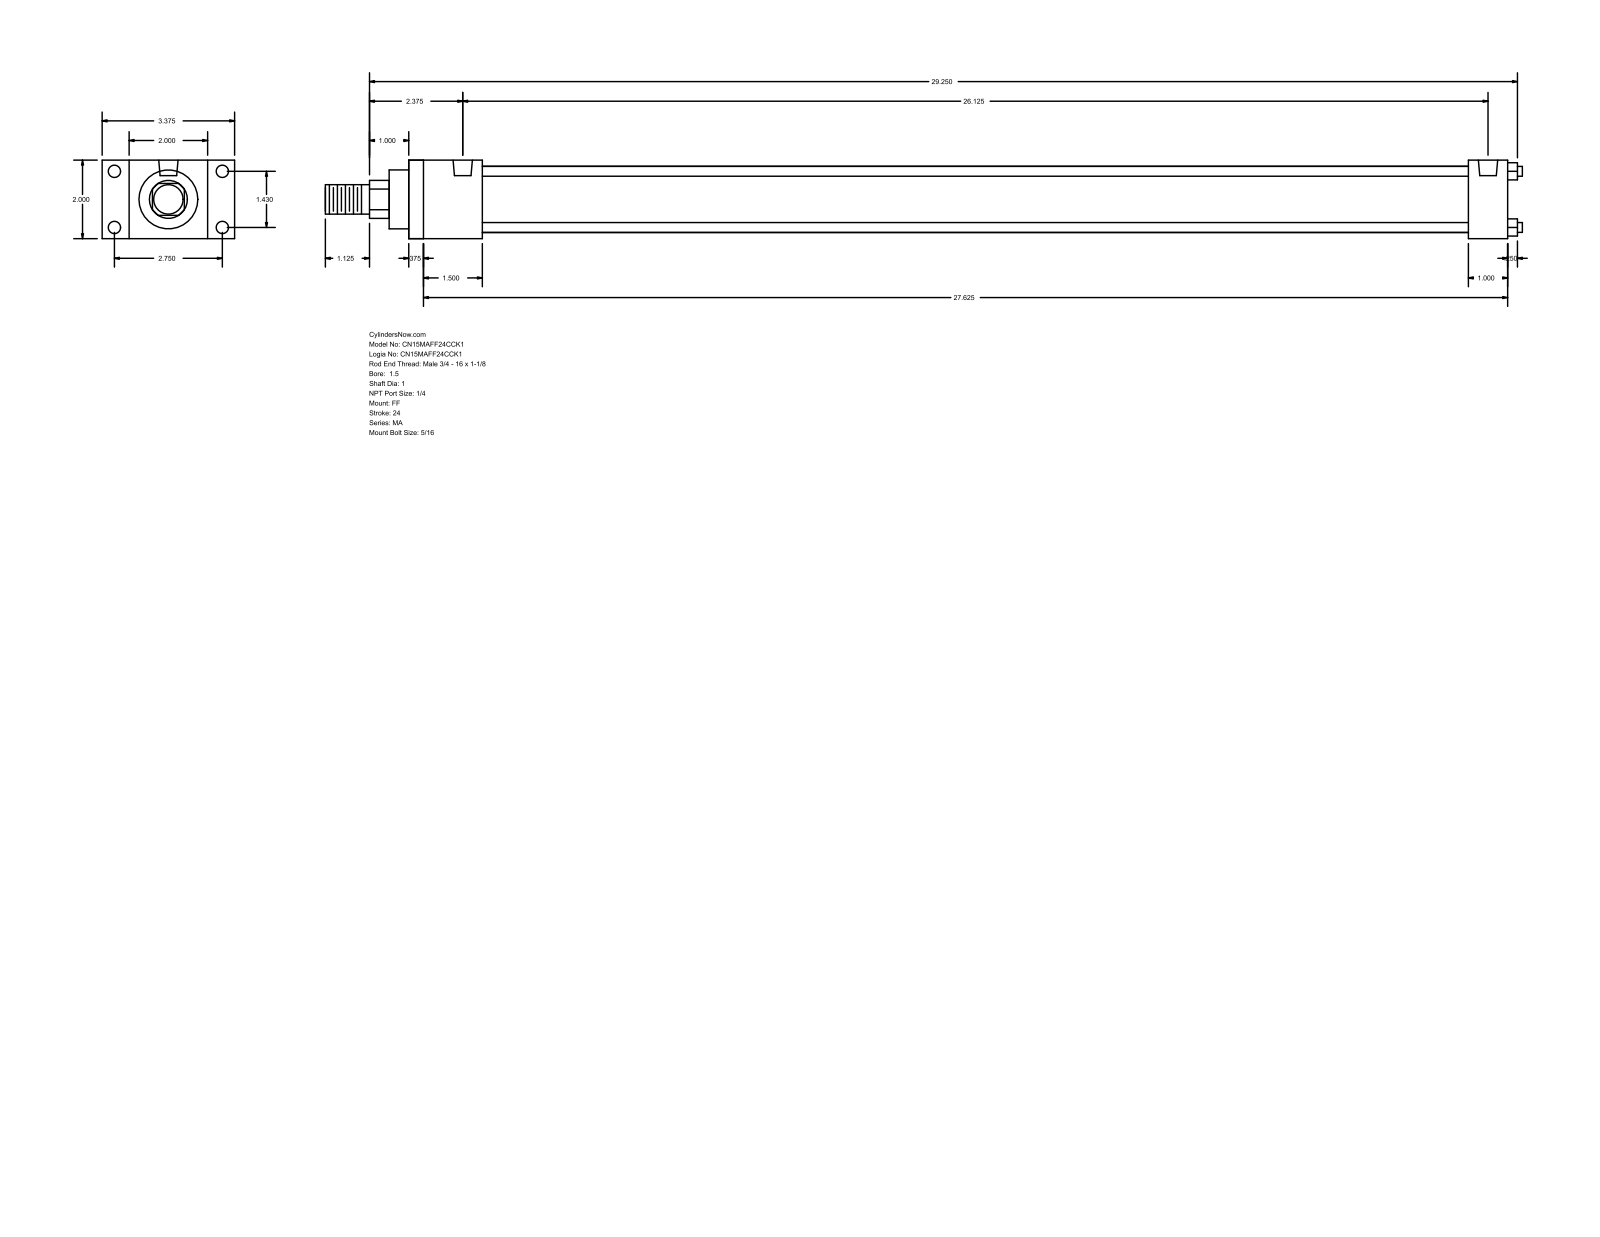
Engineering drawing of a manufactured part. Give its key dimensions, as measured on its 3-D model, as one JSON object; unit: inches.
{"part_name": "MA_FF__0150_1", "step_written_by": "GSSL Pune (CONFIG_CONTROL_DESIGN)", "units": "inches", "bodies": {"solids": 0, "faces": 92, "planar": 64, "cylindrical": 28, "other": 0}, "overall_size": [30.5, 3.375, 2], "round_holes": [[0.313, 8], [0.492, 2]], "round_bosses_or_shafts": [[0.25, 4], [1.69, 1], [1.5, 1], [1, 1], [0.75, 1]], "partial_cylinders_radius": [[0.484, 1]], "face_to_face_distances": [2, 28, 0.375, 27.625, 1, 1.875, 27, 1.5, 26.625, 25.125], "hole_center_spacings": [1.43, 2.75, 3.099, 26.125]}
